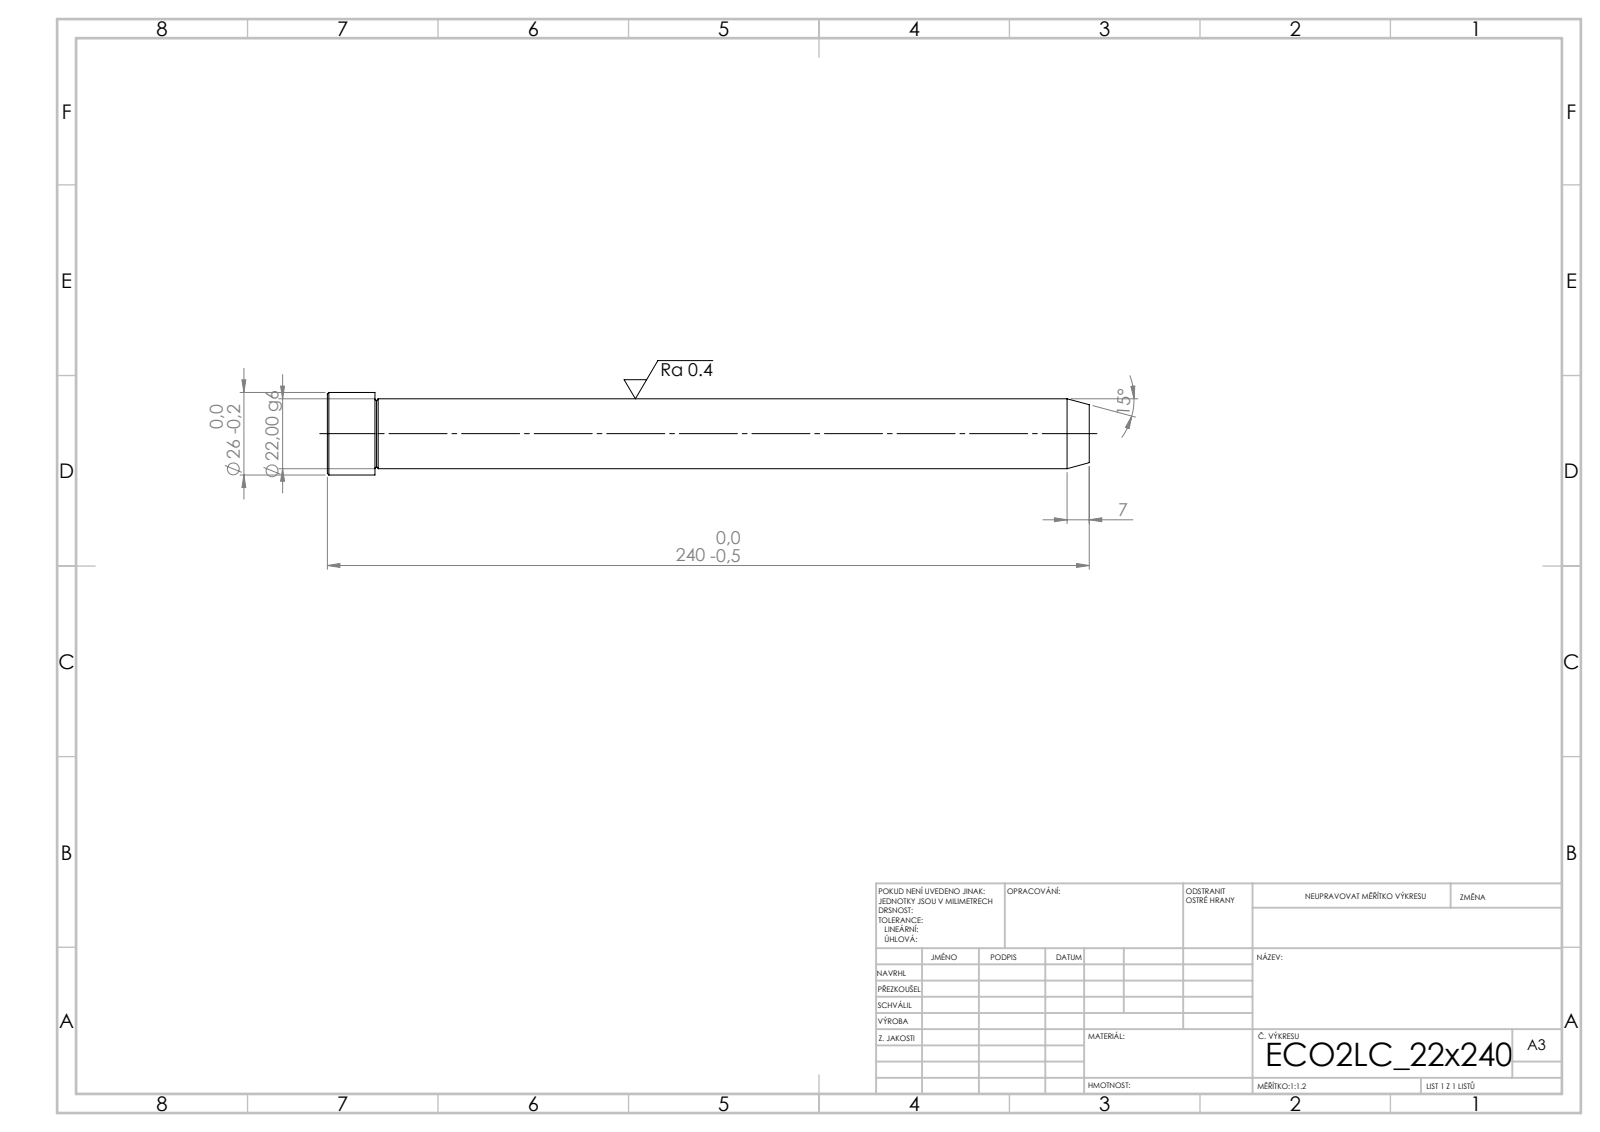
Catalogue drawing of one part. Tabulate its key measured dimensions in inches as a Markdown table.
| quantity | value |
| --- | --- |
| STEP written by | SolidWorks 2019 (CONFIG_CONTROL_DESIGN) |
| units | inches |
| bodies | 1 solid, 15 faces (3 planar, 4 cylindrical, 8 other) |
| overall size | 9.449 × 1.024 × 1.024 |
| volume | 5.677 in³ |
| surface area | 27.44 in² |
| round bosses / shafts (diameter × count) | 1.024 × 1, 0.866 × 1 |
| main face-to-face distances | 9.449, 8.858, 0.591 |
